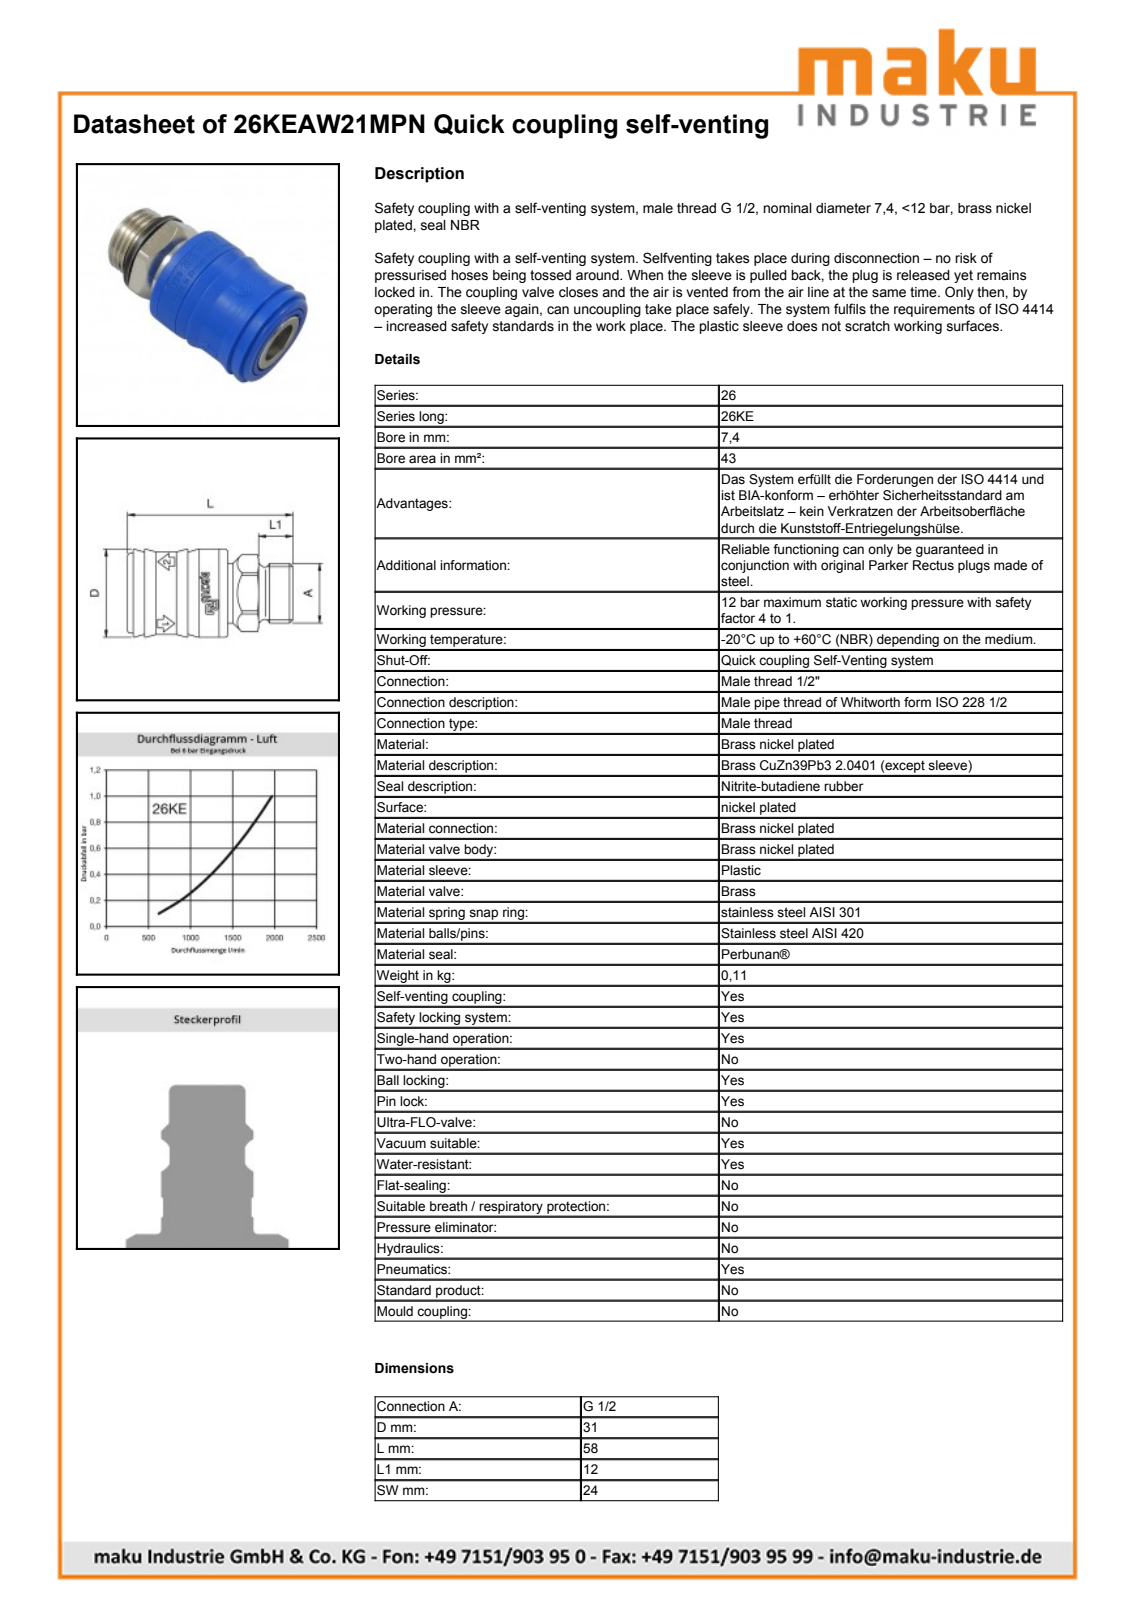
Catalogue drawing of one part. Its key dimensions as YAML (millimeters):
part_name: "D109911"
step_written_by: "Autodesk Inventor 2013 (AUTOMOTIVE_DESIGN)"
units: millimeters
bodies: {solids: 1, faces: 535, planar: 232, cylindrical: 64, other: 239}
overall_size: [58.33, 31.2, 31.1]
volume: 32131
surface_area: 7276
round_holes:
  - {diameter: 17, count: 1}
  - {diameter: 23, count: 1}
  - {diameter: 29, count: 1}
round_bosses_or_shafts:
  - {diameter: 31, count: 1}
  - {diameter: 28, count: 1}
  - {diameter: 21, count: 1}
  - {diameter: 20.95, count: 1}
partial_cylinders:
  - {radius: 13.53, count: 1}
  - {radius: 13.82, count: 1}
  - {radius: 15.6, count: 1}
face_to_face_distances: [31.97, 58.1, 26.13, 2, 30.2, 24, 32.2, 58.33, 1.77, 56.33]
